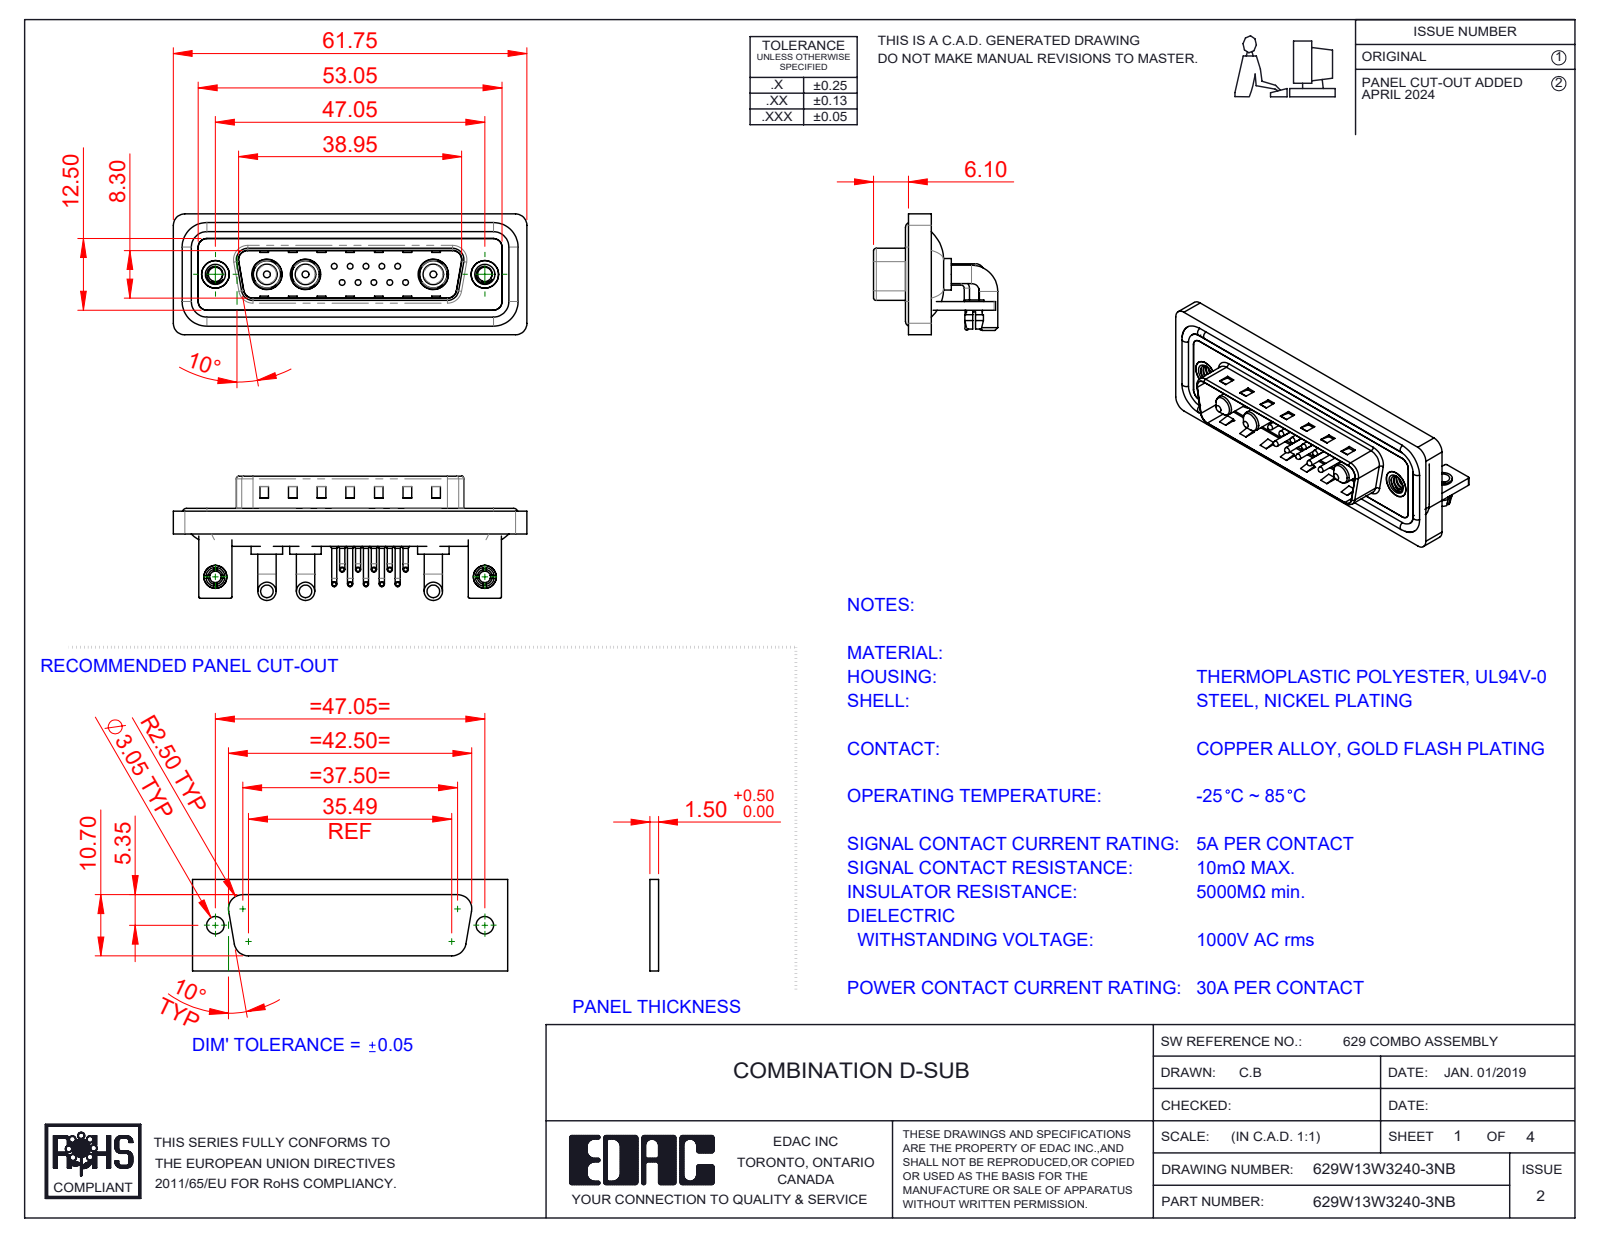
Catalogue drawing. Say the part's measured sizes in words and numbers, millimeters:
The part is named "629W13W3140-3NB; 629Combo Board Lock; 629Combo Stabilizer Bracket; 629Combo Waterproof Housing_25 Contacts (+7 more)". Its 3-D file was written by "SolidWorks 2023 (CONFIG_CONTROL_DESIGN)". It is 27 solids with 1842 faces: 947 planar, 661 cylindrical and 234 other. Overall it measures 61.75 by 21.7 by 21.1 millimeters. Its volume is 8 002 cubic millimeters and its surface area 13 350 square millimeters. Round holes: 12 of diameter 2, 10 of diameter 0.75, 10 of diameter 1.6, 4 of diameter 2.5, 3 of diameter 4.85, 3 of diameter 5.3, 2 of diameter 3.2, 2 of diameter 4, 2 of diameter 4.8, 2 of diameter 5. Round bosses or shafts: 20 of diameter 0.9, 10 of diameter 1.5, 10 of diameter 1, 10 of diameter 0.65, 6 of diameter 3.2, 4 of diameter 1.6, 3 of diameter 5.5, 3 of diameter 5.2. Partial cylindrical surfaces (rounded edges, fillets, slot ends): 19 of radius 2, 18 of radius 1.5, 16 of radius 0.25, 10 of radius 1.01, 9 of radius 0.5, 8 of radius 1.6, 4 of radius 0.6, 4 of radius 0.65. The main face-to-face distances are 0.4, 0.8, 1.5, 2.9, 2.1, 1.1, 4.1, 1.6, 3.7, 4.5. The hole center spacings are 3.16, 2.77, 5.04, 5.54, 7.49, 5.03, 8.31, 10.11.
